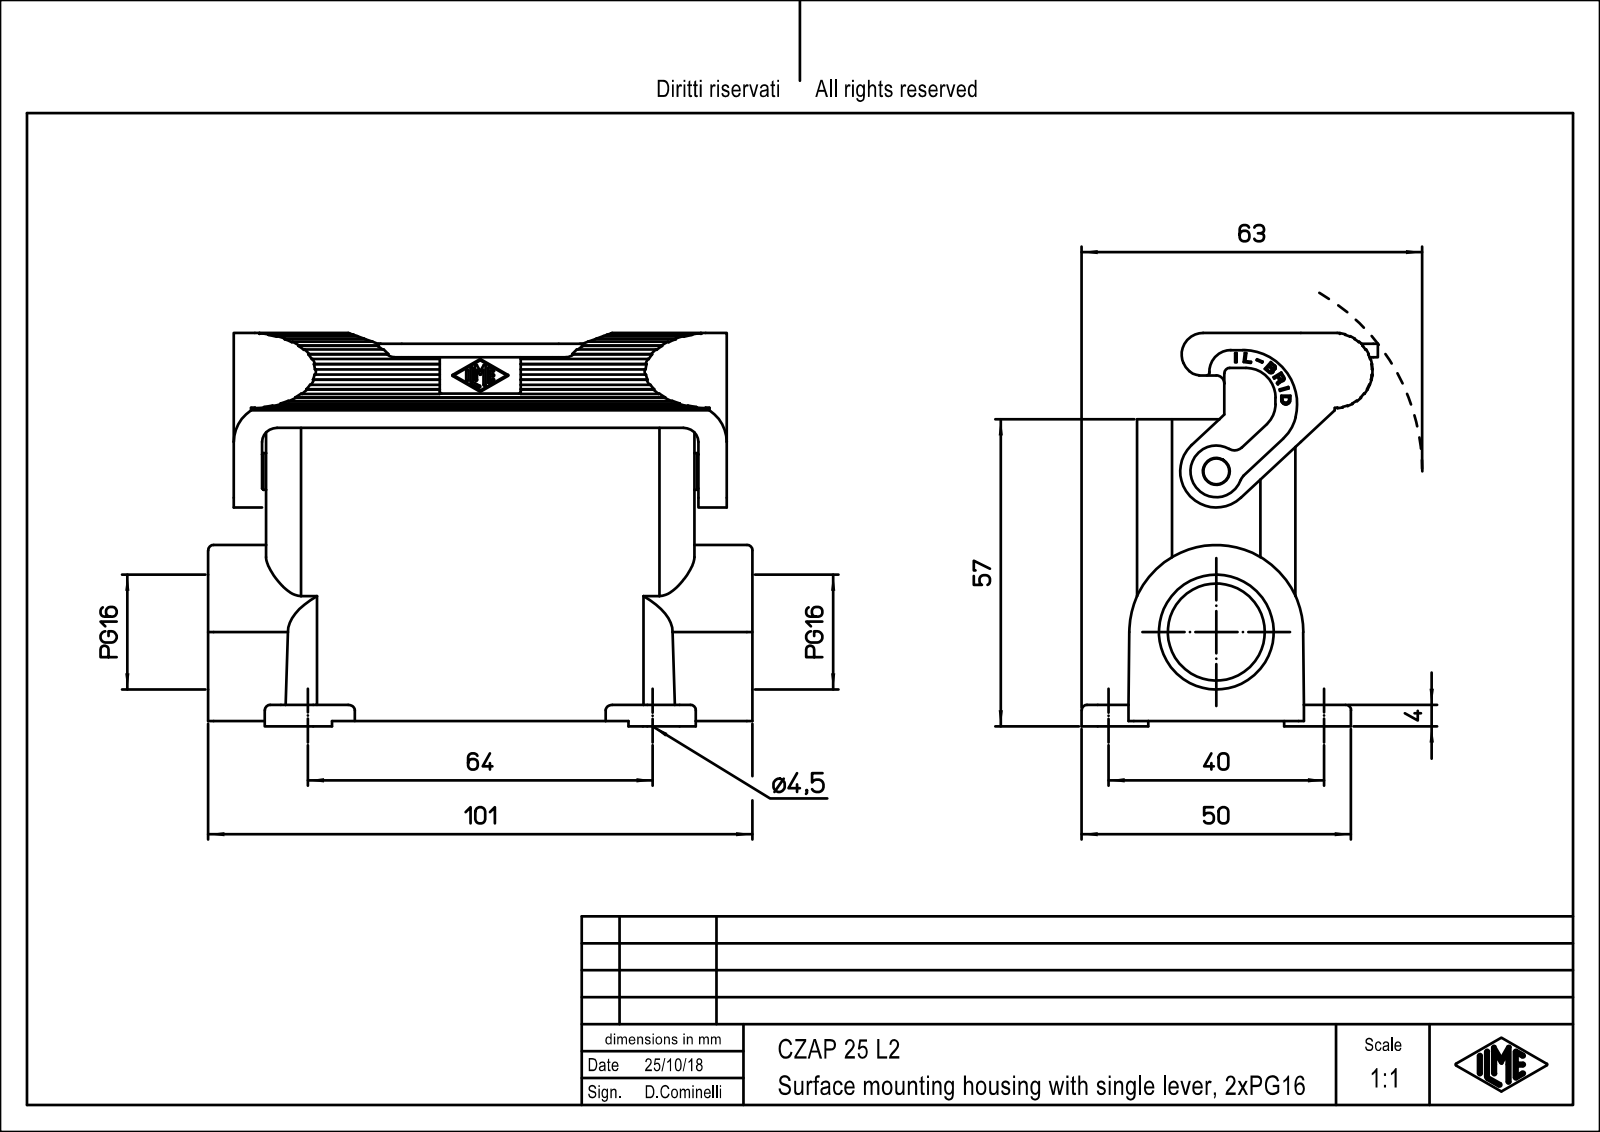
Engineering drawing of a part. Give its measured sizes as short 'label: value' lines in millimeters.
name: CZAP_25_L2
written by: PTC Creo Elements/Direct Modeling 19.0E 27-Jun-2016 (C) Parametric Technology GmbH (AUTOMOTIVE_DESIGN)
unit: mm
bodies: 1 solid, 414 faces (219 planar, 181 cylindrical, 14 other)
size: 101 × 73 × 55
volume: 71 768 mm³; area: 39 935 mm²
holes: 4× ⌀3, 4× ⌀4.5, 1× ⌀18, 1× ⌀21.3
bosses: 1× ⌀6.8, 1× ⌀4.8
rounds: 17× R1, 15× R0.2, 8× R3.5, 5× R3, 4× R3.2, 4× R6.5, 3× R0.1, 2× R0.3
face distances: 2.76, 26.64, 29.4, 23.88, 3, 33.2, 30.44, 6.56, 3.8, 10
hole spacings: 12.04, 28.02, 66.1, 70.77, 16, 40, 64, 66
